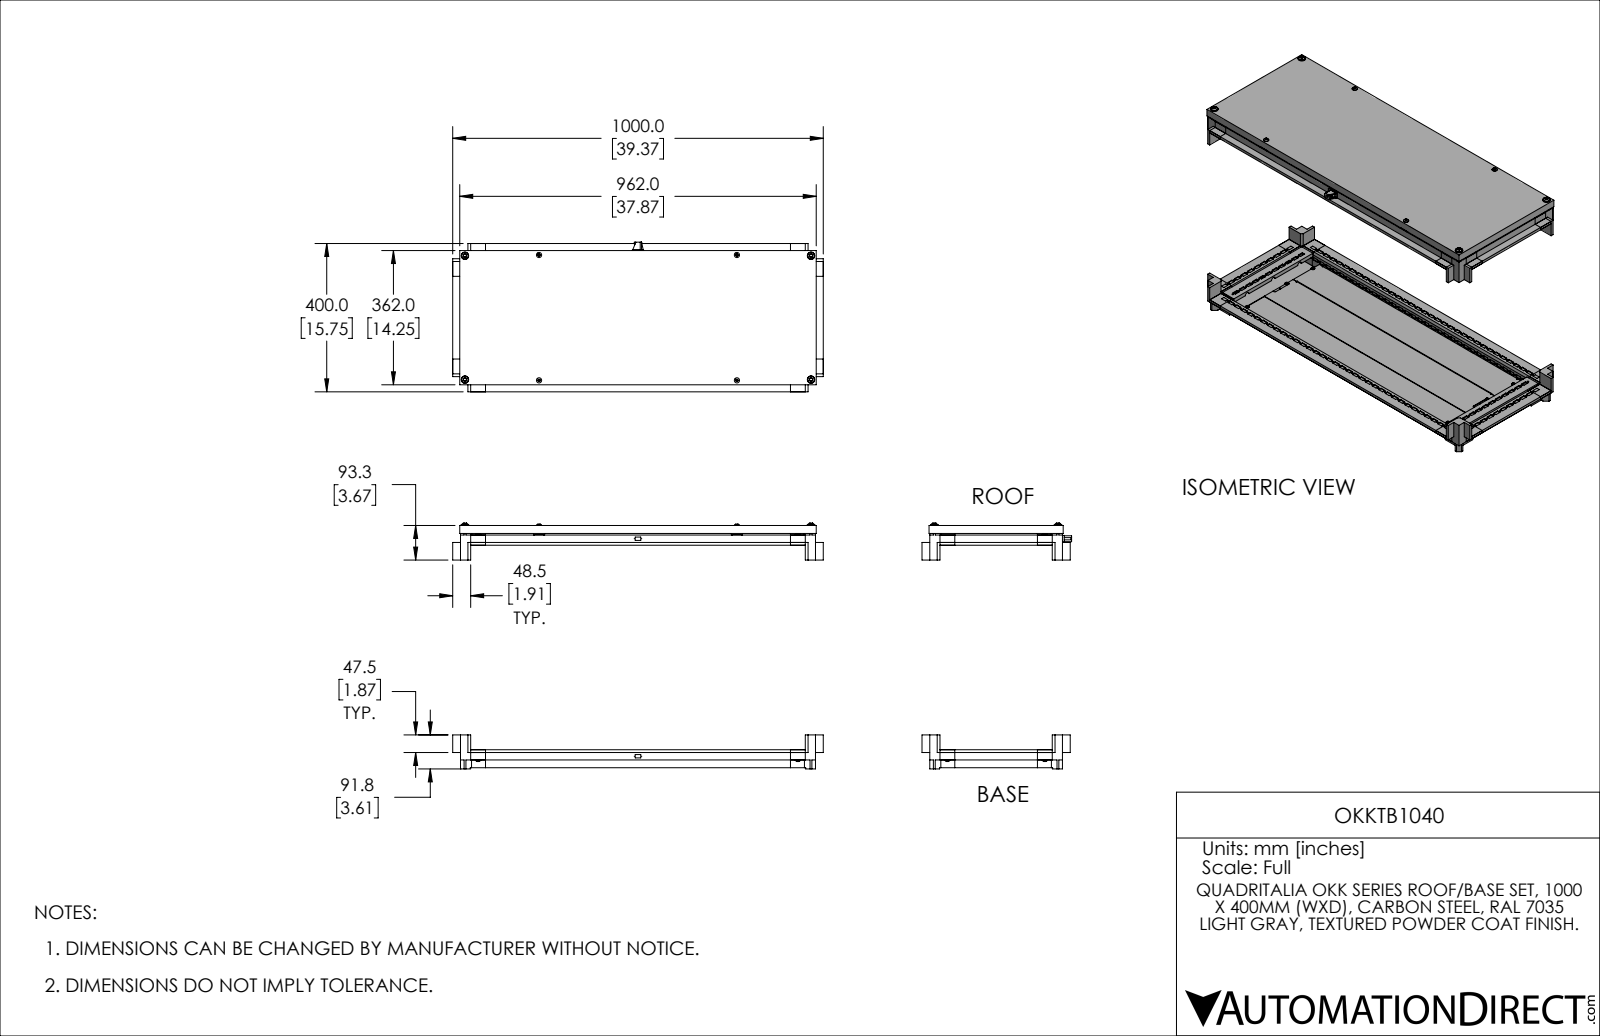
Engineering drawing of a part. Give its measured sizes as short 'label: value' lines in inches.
name: OKKTB1040
written by: SolidWorks 2021 (AUTOMOTIVE_DESIGN)
unit: in
bodies: 78 solids, 5167 faces (3905 planar, 1031 cylindrical, 231 other)
size: 39.37 × 26.095 × 15.894
volume: 477.1 in³; area: 4 510 in²
holes: 220× ⌀0.167, 12× ⌀0.01, 11× ⌀0.354, 8× ⌀0.154, 5× ⌀0.194, 5× ⌀0.295, 3× ⌀0.194, 3× ⌀0.323
bosses: 15× ⌀0.551, 11× ⌀0.315, 9× ⌀0.394, 8× ⌀0.236, 6× ⌀0.197, 4× ⌀0.787, 4× ⌀0.472, 1× ⌀0.276
rounds: 312× R0.02, 24× R0.039, 20× R0.008, 16× R0.01, 12× R0.177, 8× R0.138, 6× R0.079, 6× R0.217
face distances: 0.059, 24.796, 24.855, 0.787, 1.083, 0.295, 0.807, 24.737, 0.098, 0.689
hole spacings: 0.984, 1.969, 2.953, 3.937, 4.921, 5.906, 6.89, 7.874
